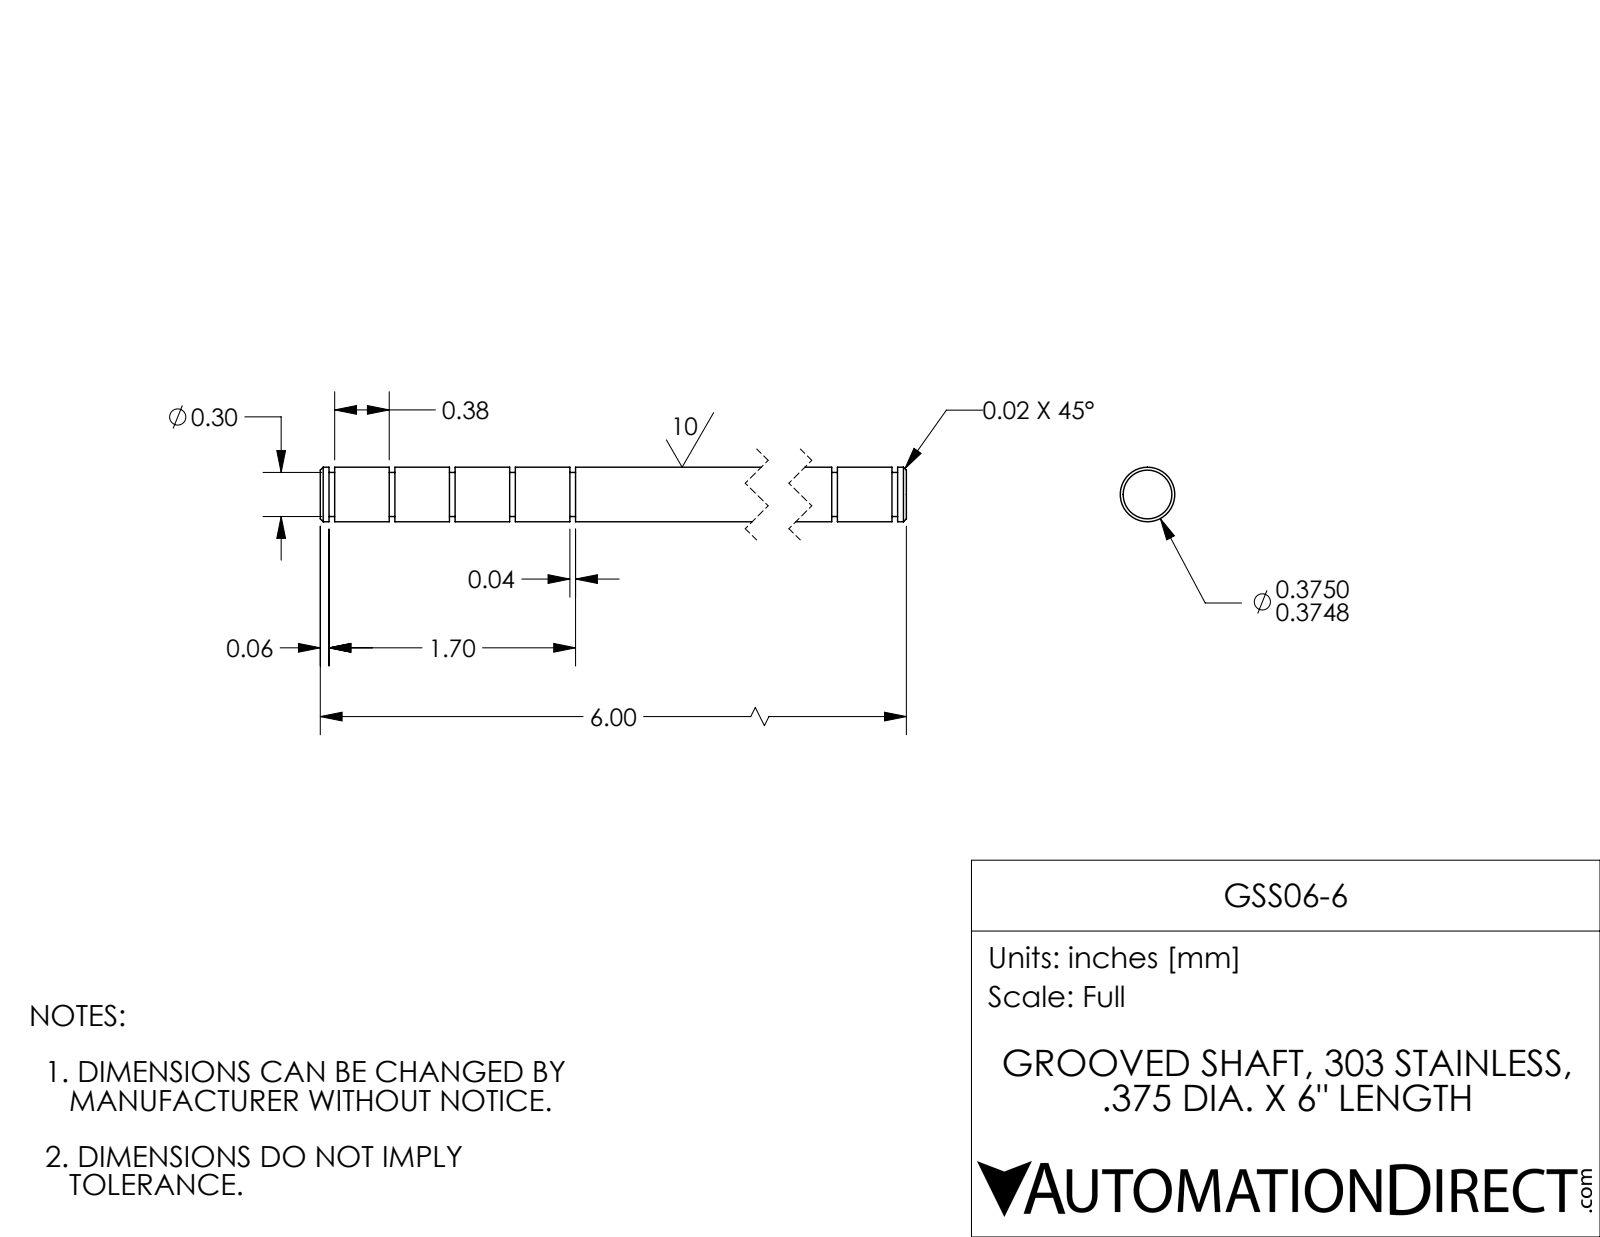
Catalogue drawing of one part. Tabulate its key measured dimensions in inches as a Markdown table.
| quantity | value |
| --- | --- |
| part name | GSS06-6 |
| STEP written by | SolidWorks 2017 (AUTOMOTIVE_DESIGN) |
| units | inches |
| bodies | 1 solid, 50 faces (16 planar, 30 cylindrical, 4 other) |
| overall size | 6 × 0.375 × 0.375 |
| volume | 0.652 in³ |
| surface area | 7.736 in² |
| round bosses / shafts (diameter × count) | 0.375 × 1, 0.303 × 1 |
| main face-to-face distances | 0.414, 0.039, 1.242, 5.427, 0.828, 5.013, 4.185, 0.453, 0.375, 6 |
